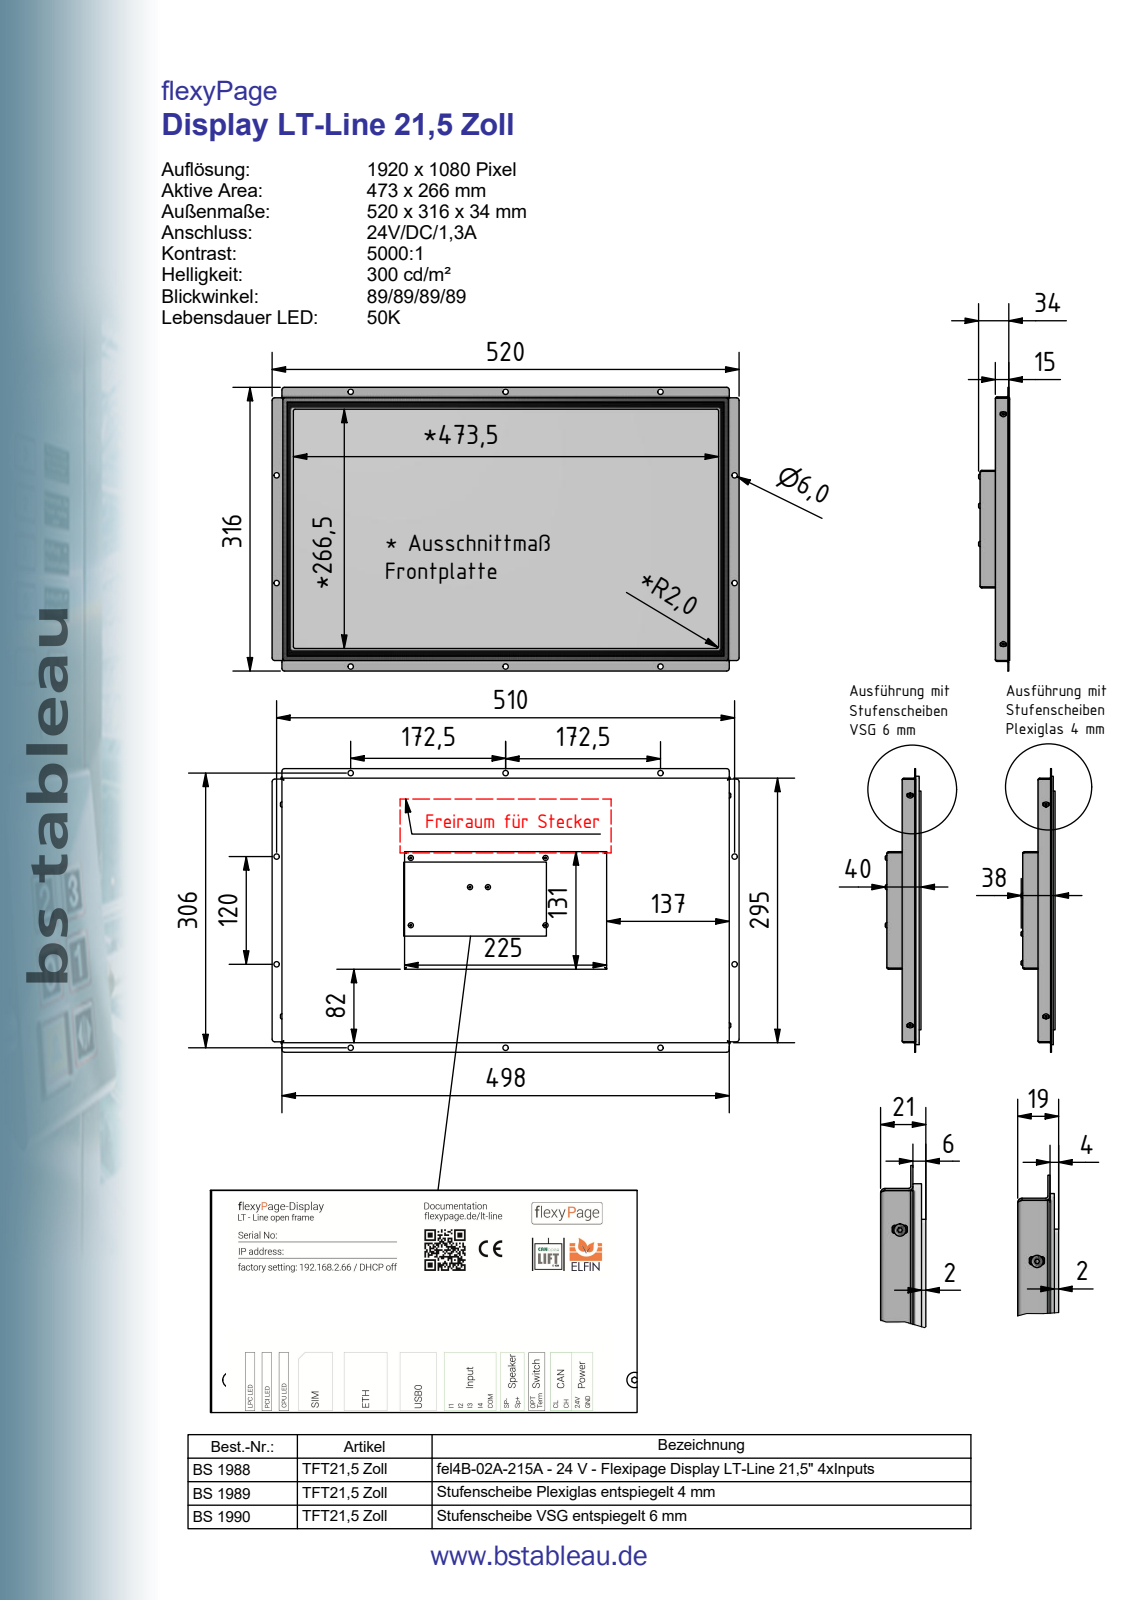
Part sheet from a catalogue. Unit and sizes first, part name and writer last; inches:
Units: inches
Overall size (bounding box): 20.472 × 12.441 × 1.364
Round holes (diameter × count): ⌀0.236 ×10, ⌀0.097 ×8, ⌀0.126 ×4, ⌀0.136 ×4, ⌀0.173 ×4, ⌀0.059 ×3, ⌀0.122 ×2
Round bosses / shafts (diameter × count): ⌀0.016 ×11, ⌀0.224 ×10, ⌀0.118 ×10, ⌀0.213 ×4
Partial cylindrical surfaces — rounded edges, fillets, slot ends (radius × count): R0.039 ×28, R0.059 ×24, R0.012 ×21, R0.079 ×17, R0.024 ×9, R0.008 ×8, R0.118 ×8, R0.02 ×6
Main face-to-face distances: 0.039, 0.512, 0.551, 0.079, 0.591, 0.709, 0.669, 1.22, 0.748, 0.63
Hole centre spacings: 4.894, 6.791, 8.993, 10.686, 13.081, 13.83, 17.224, 18.804
Volume: 130.6 in³ · Surface area: 1 223 in²
Bodies: 32 solids, 1224 faces (774 planar, 209 cylindrical, 241 other)
Part name (STEP PRODUCT): 20000089 fel4B-02A-21,5 Zoll LT-Line; 00003290 fel4B4-02A-21,5 Zoll LT-Line-UT; 00003295 FPC04 Platine; 00003435 V-S0-3,5-M3x4 (+7 more)
STEP written by: Autodesk Inventor 2019 (AUTOMOTIVE_DESIGN)
